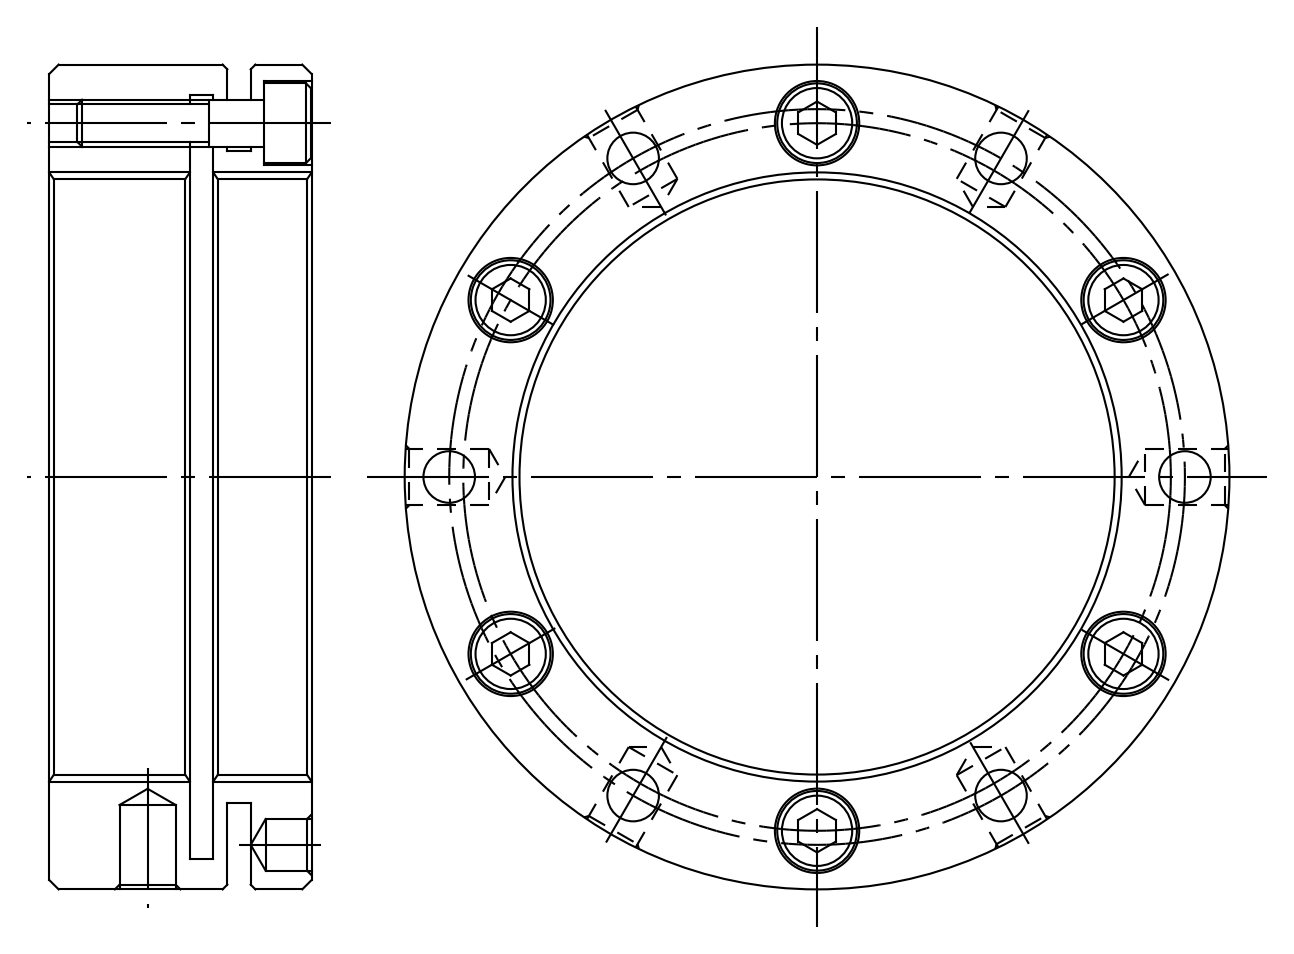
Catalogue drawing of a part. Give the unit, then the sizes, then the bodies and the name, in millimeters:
Units: millimetres
Overall size (bounding box): 88 × 88 × 28
Round holes (diameter × count): ⌀4.13 ×6, ⌀5.3 ×6, ⌀5.5 ×6, ⌀9 ×6, ⌀6 ×3, ⌀65 ×1, ⌀82 ×1
Round bosses / shafts (diameter × count): ⌀8.5 ×6, ⌀5 ×6, ⌀88 ×1, ⌀70 ×1
Main face-to-face distances: 2.5, 4, 14, 28, 18, 10, 20.5, 7.5, 6.5, 16.5
Hole centre spacings: 38, 39.25, 74.62, 20.03, 54.63, 65.82, 20.04, 54.64
Volume: 65 099 mm³ · Surface area: 33 911 mm²
Bodies: 7 solids, 204 faces (72 planar, 108 cylindrical, 24 other)
Part name (STEP PRODUCT): FKD FAN65; M5X20_default
STEP written by: SolidWorks 2012 (CONFIG_CONTROL_DESIGN)
